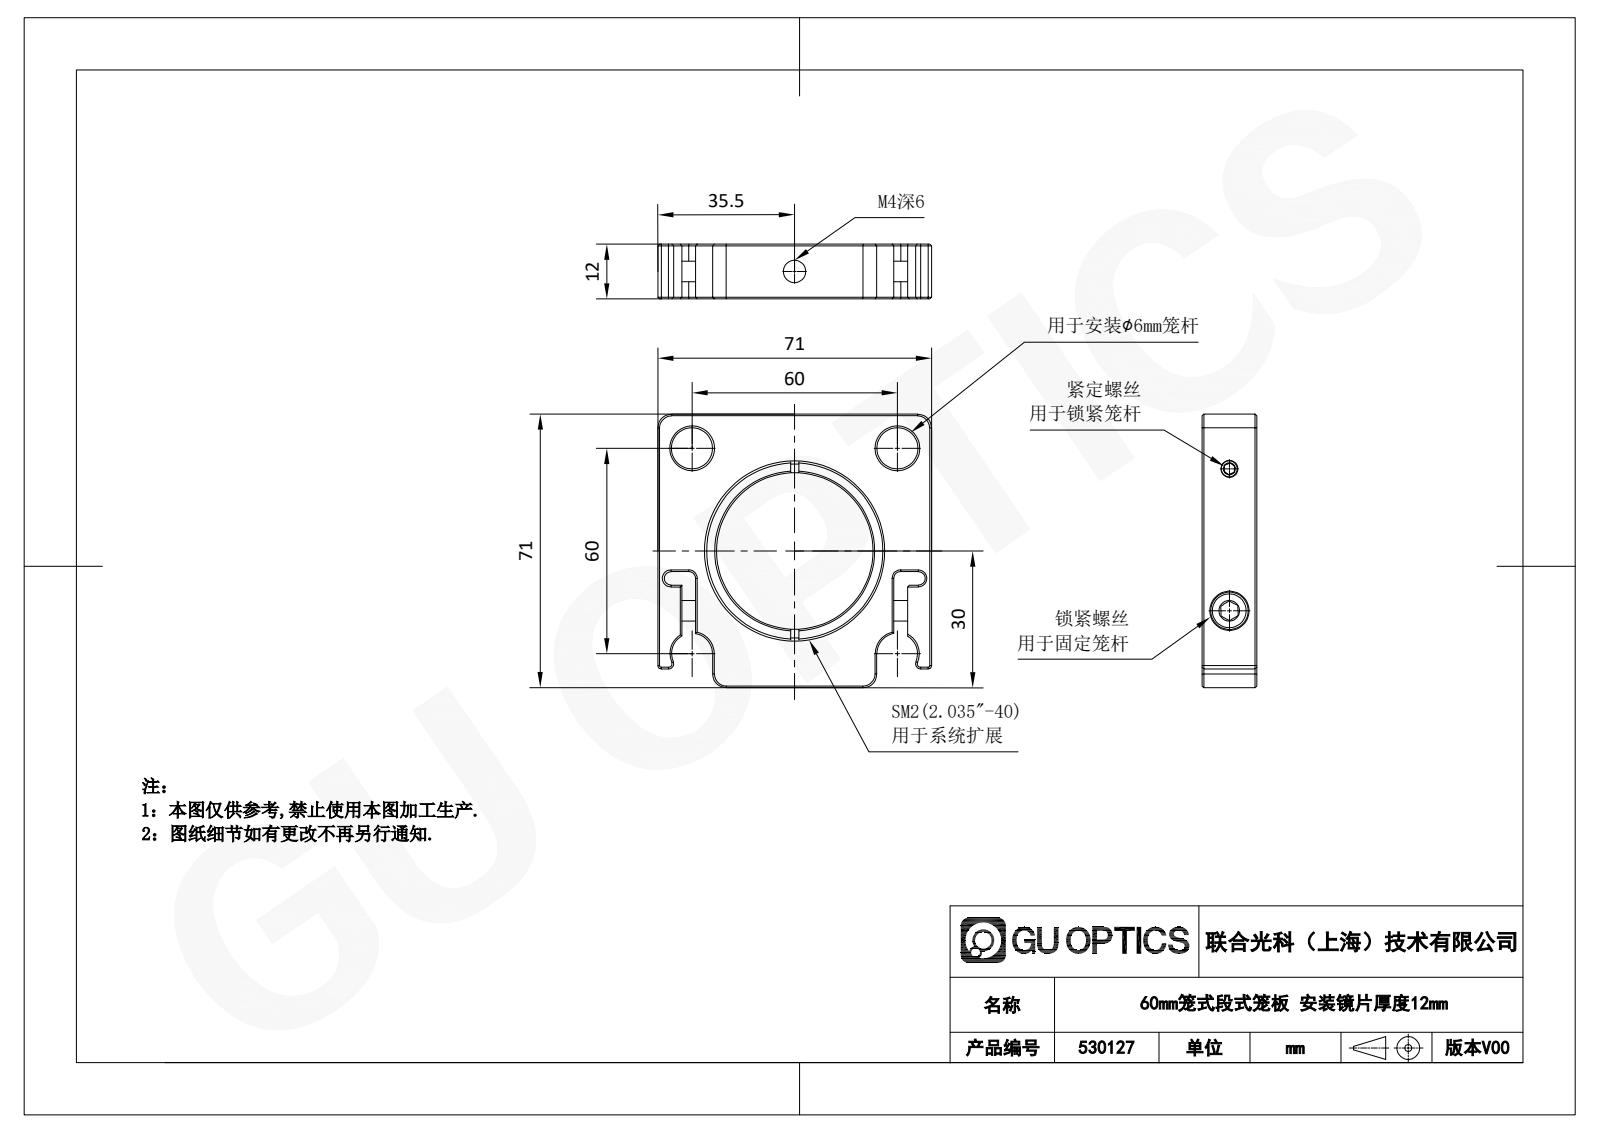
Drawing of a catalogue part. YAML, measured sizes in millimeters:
part_name: "530127"
step_written_by: "SolidWorks 2020 (CONFIG_CONTROL_DESIGN)"
units: millimeters
bodies: {solids: 7, faces: 223, planar: 112, cylindrical: 35, other: 76}
overall_size: [71.12, 71.12, 12.7]
volume: 34891
surface_area: 15463
round_holes:
  - {diameter: 2.5, count: 2}
  - {diameter: 6, count: 2}
  - {diameter: 6.35, count: 2}
  - {diameter: 3.3, count: 1}
  - {diameter: 3.4, count: 1}
  - {diameter: 5.99, count: 1}
  - {diameter: 48.3, count: 1}
  - {diameter: 51.69, count: 1}
round_bosses_or_shafts:
  - {diameter: 3, count: 2}
  - {diameter: 51.69, count: 1}
  - {diameter: 5.5, count: 1}
partial_cylinders:
  - {radius: 2.54, count: 2}
  - {radius: 3.01, count: 2}
  - {radius: 3.17, count: 2}
  - {radius: 1.59, count: 1}
  - {radius: 1.59, count: 1}
face_to_face_distances: [12.7, 71.12, 2.5, 10.2, 6.75, 64.37, 7.7, 60, 4.37, 66.75]
hole_center_spacings: [42.43, 46.54, 35.67, 35.68, 51.69, 60, 63.25, 77.2]
